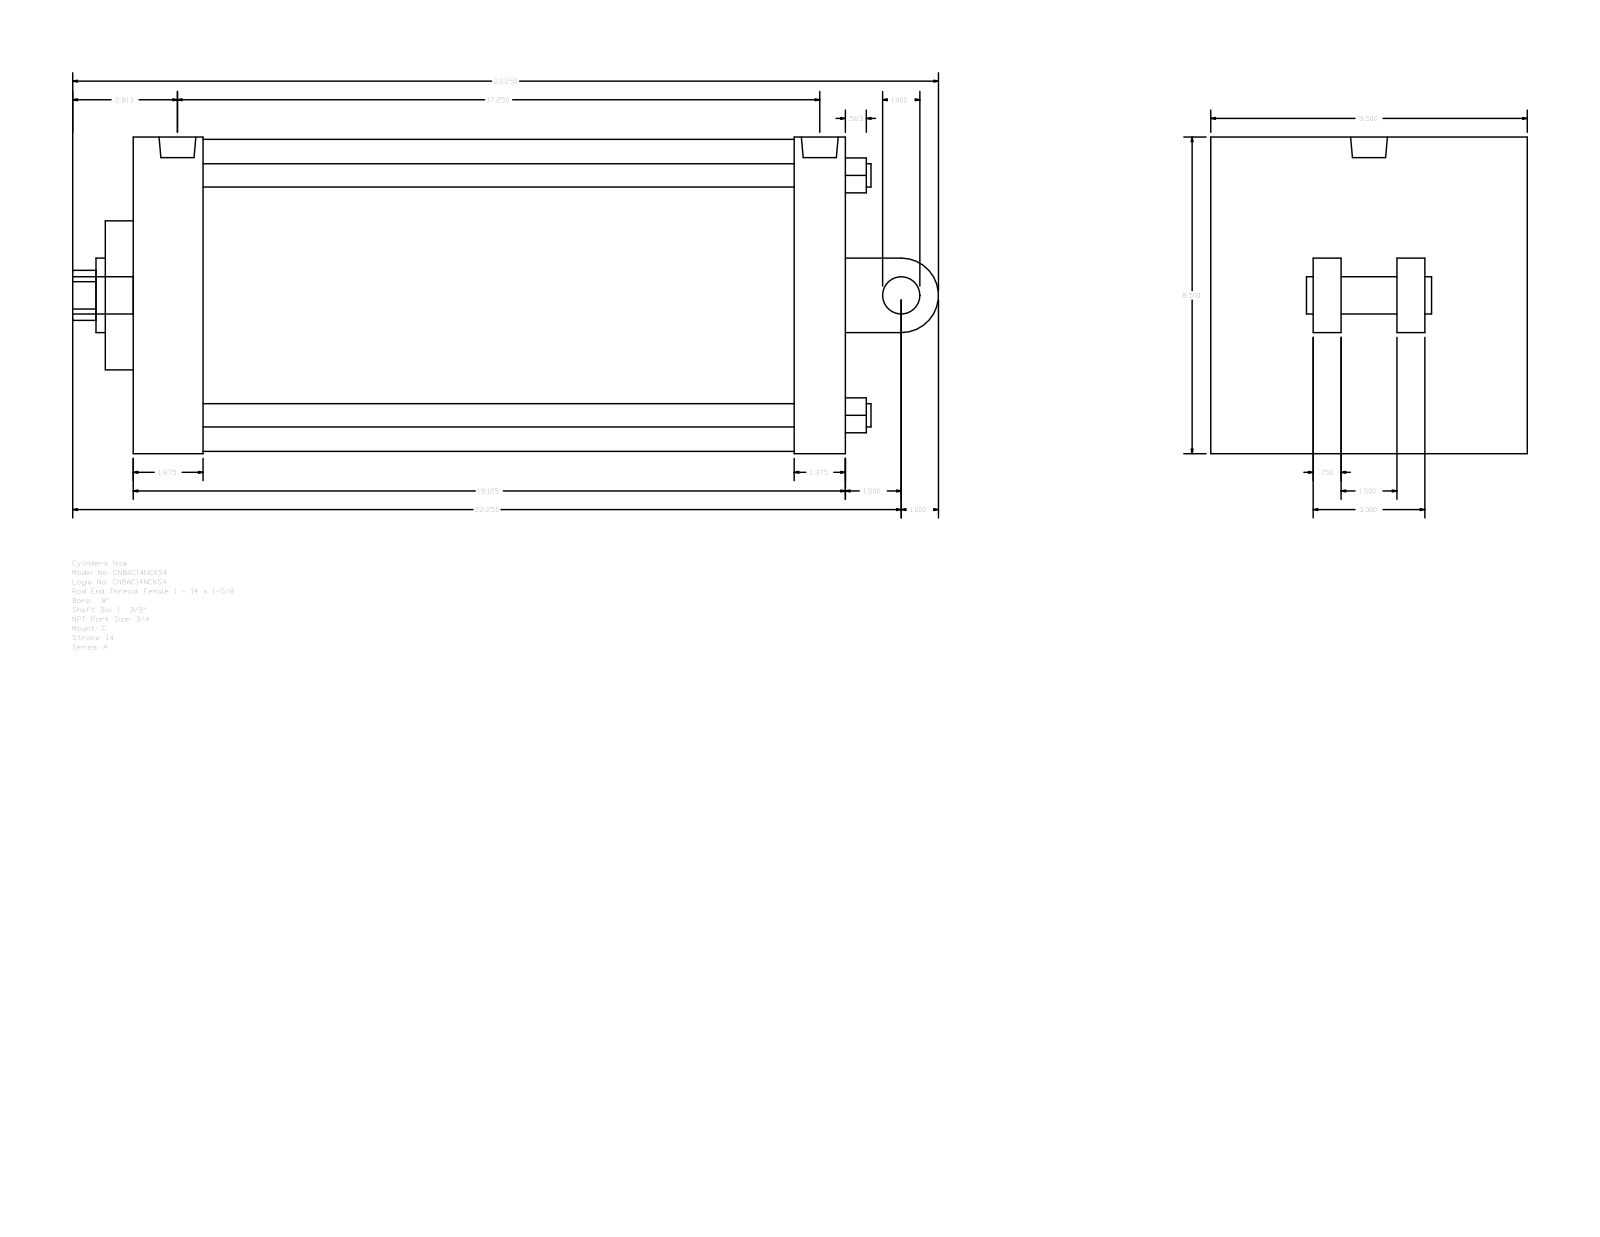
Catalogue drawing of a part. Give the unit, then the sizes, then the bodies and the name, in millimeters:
Units: millimetres
Overall size (bounding box): 590.55 × 215.9 × 215.9
Round holes (diameter × count): ⌀15.88 ×4, ⌀15.08 ×2, ⌀25.12 ×1, ⌀34.92 ×1, ⌀50.8 ×1, ⌀212.72 ×1
Round bosses / shafts (diameter × count): ⌀25.4 ×2, ⌀15.08 ×2, ⌀25.12 ×1
Partial cylindrical surfaces — rounded edges, fillets, slot ends (radius × count): R17.06 ×1, R25.4 ×1
Main face-to-face distances: 485.78, 215.9, 57.15, 47.63, 438.15, 450.85, 403.22, 34.93, 88.9, 69.85
Hole centre spacings: 115.67, 163.58, 231.34, 6.35
Bodies: 0 solids, 104 faces (75 planar, 29 cylindrical, 0 other)
Part name (STEP PRODUCT): A_C__0800_1.375
STEP written by: GSSL Pune (CONFIG_CONTROL_DESIGN)
